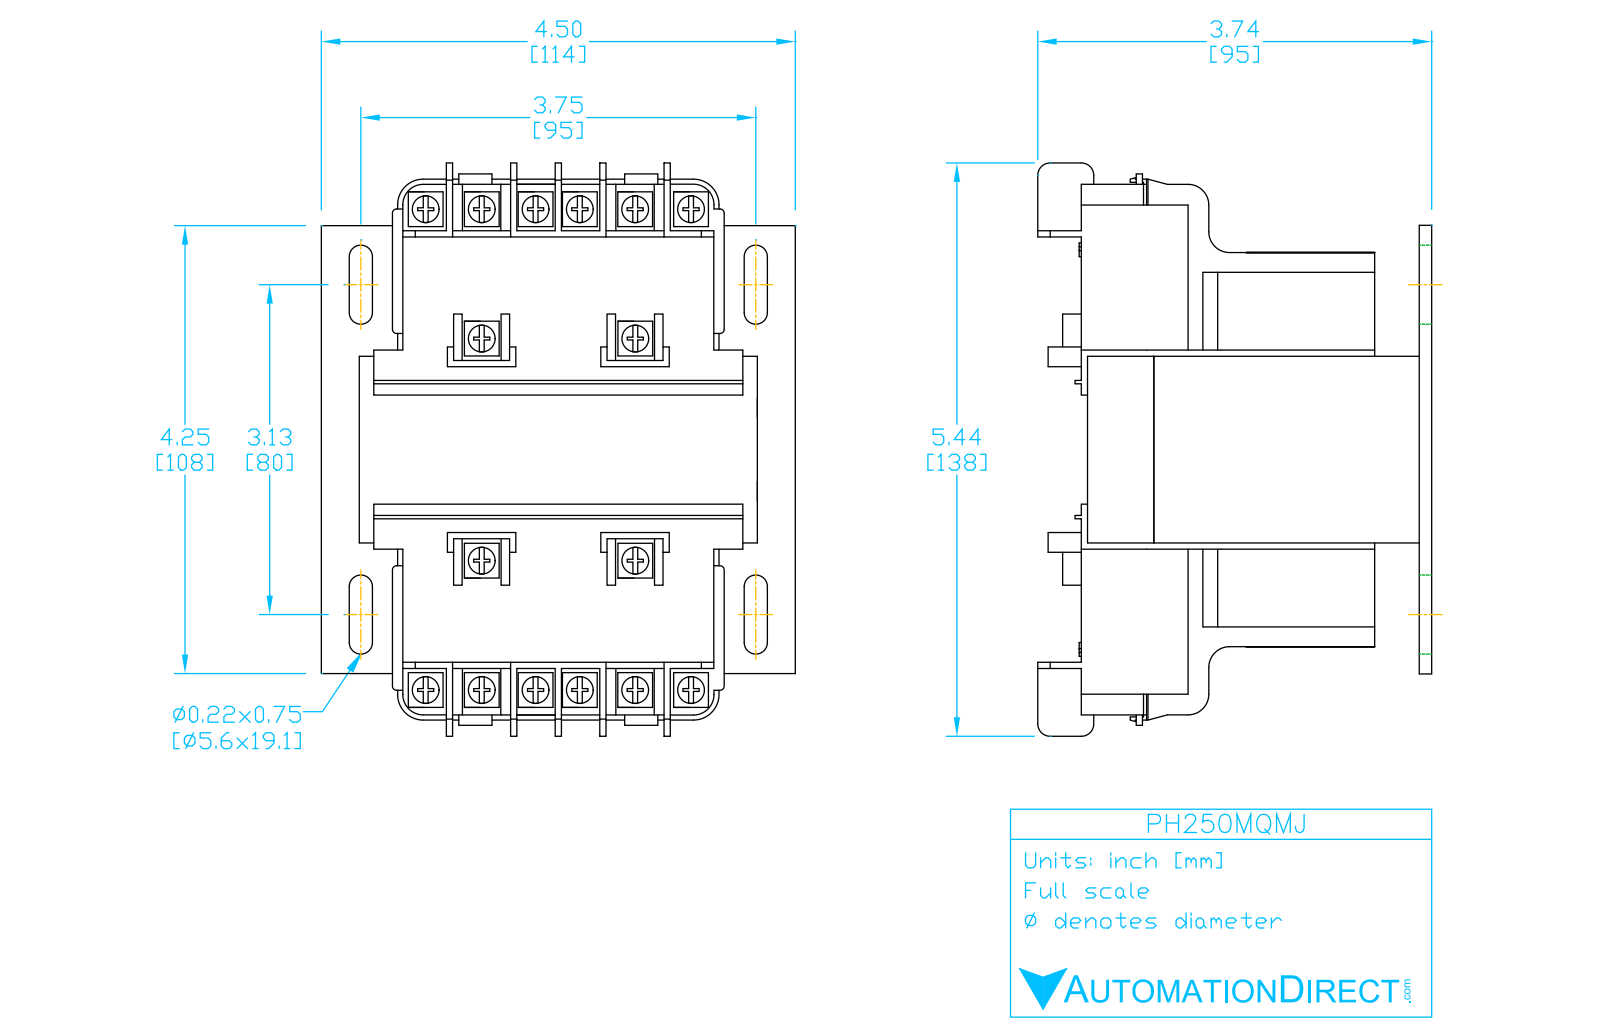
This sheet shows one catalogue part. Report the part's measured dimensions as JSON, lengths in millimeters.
{"part_name": "PH250MQMJ", "step_written_by": "SolidWorks 2017 (AUTOMOTIVE_DESIGN)", "units": "millimeters", "bodies": {"solids": 9, "faces": 474, "planar": 324, "cylindrical": 126, "other": 24}, "overall_size": [135.9, 114.3, 95], "volume_mm3": 755400, "surface_area_mm2": 125900, "round_holes": [[4, 4]], "partial_cylinders_radius": [[1, 48], [5, 12], [1.3, 10], [2.8, 8], [2.5, 4], [4.9, 4], [6.2, 4], [12, 2]], "face_to_face_distances": [1.5, 46.5, 45, 1.8, 64, 65.8, 26.2, 3, 92, 28], "hole_center_spacings": [31.8, 85.7, 91.4]}
